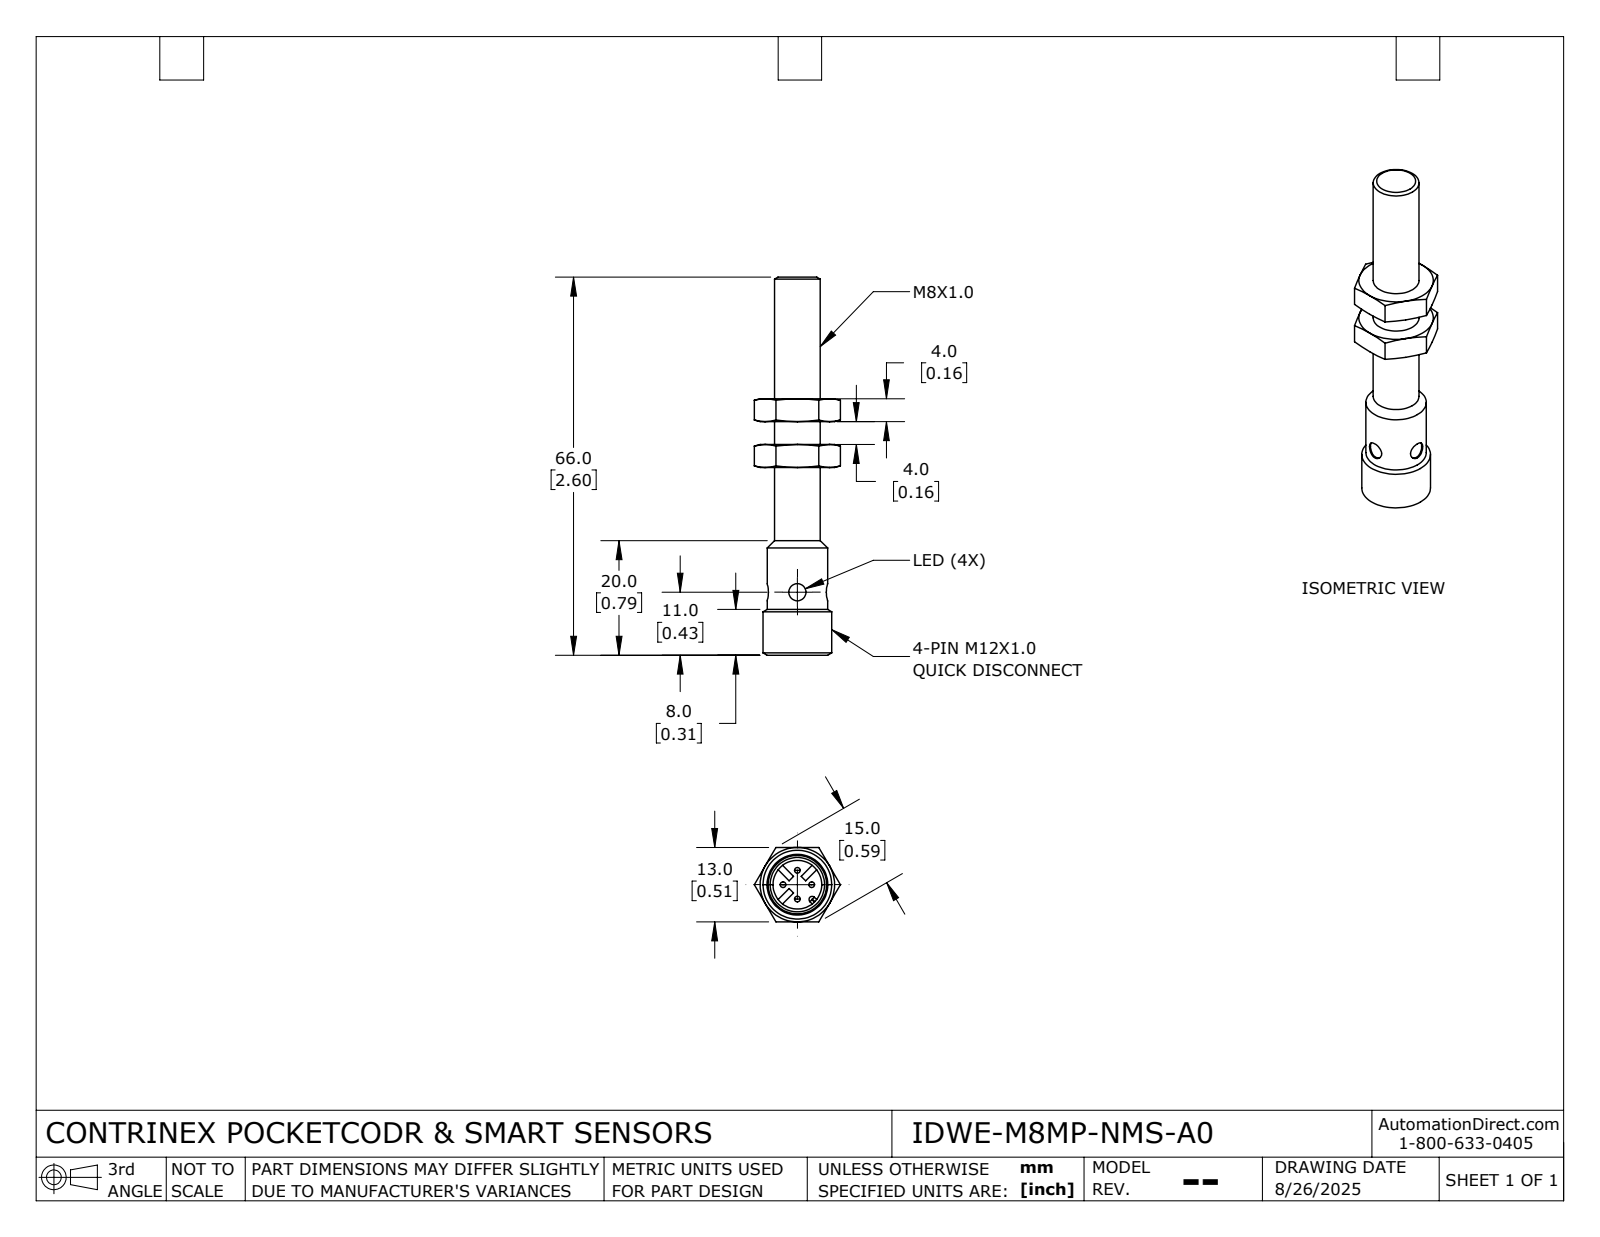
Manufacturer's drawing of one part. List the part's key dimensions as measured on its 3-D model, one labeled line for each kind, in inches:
Part name (STEP PRODUCT): IDWE-M8MP-NMS-A0
STEP written by: SolidWorks 2024 (AUTOMOTIVE_DESIGN)
Units: inches
Bodies: 3 solids, 115 faces (35 planar, 33 cylindrical, 47 other)
Overall size (bounding box): 2.598 × 0.591 × 0.512
Volume: 0.281 in³ · Surface area: 5.116 in²
Round holes (diameter × count): ⌀0.118 ×2, ⌀0.272 ×1, ⌀0.335 ×1
Round bosses / shafts (diameter × count): ⌀0.039 ×4, ⌀0.472 ×1, ⌀0.415 ×1, ⌀0.315 ×1
Partial cylindrical surfaces — rounded edges, fillets, slot ends (radius × count): R0.02 ×2, R0.022 ×1, R0.199 ×1
Main face-to-face distances: 0.157, 0.512, 0.315, 0.472, 1.42, 1.263, 1.105, 0.948, 0.835, 0.993
